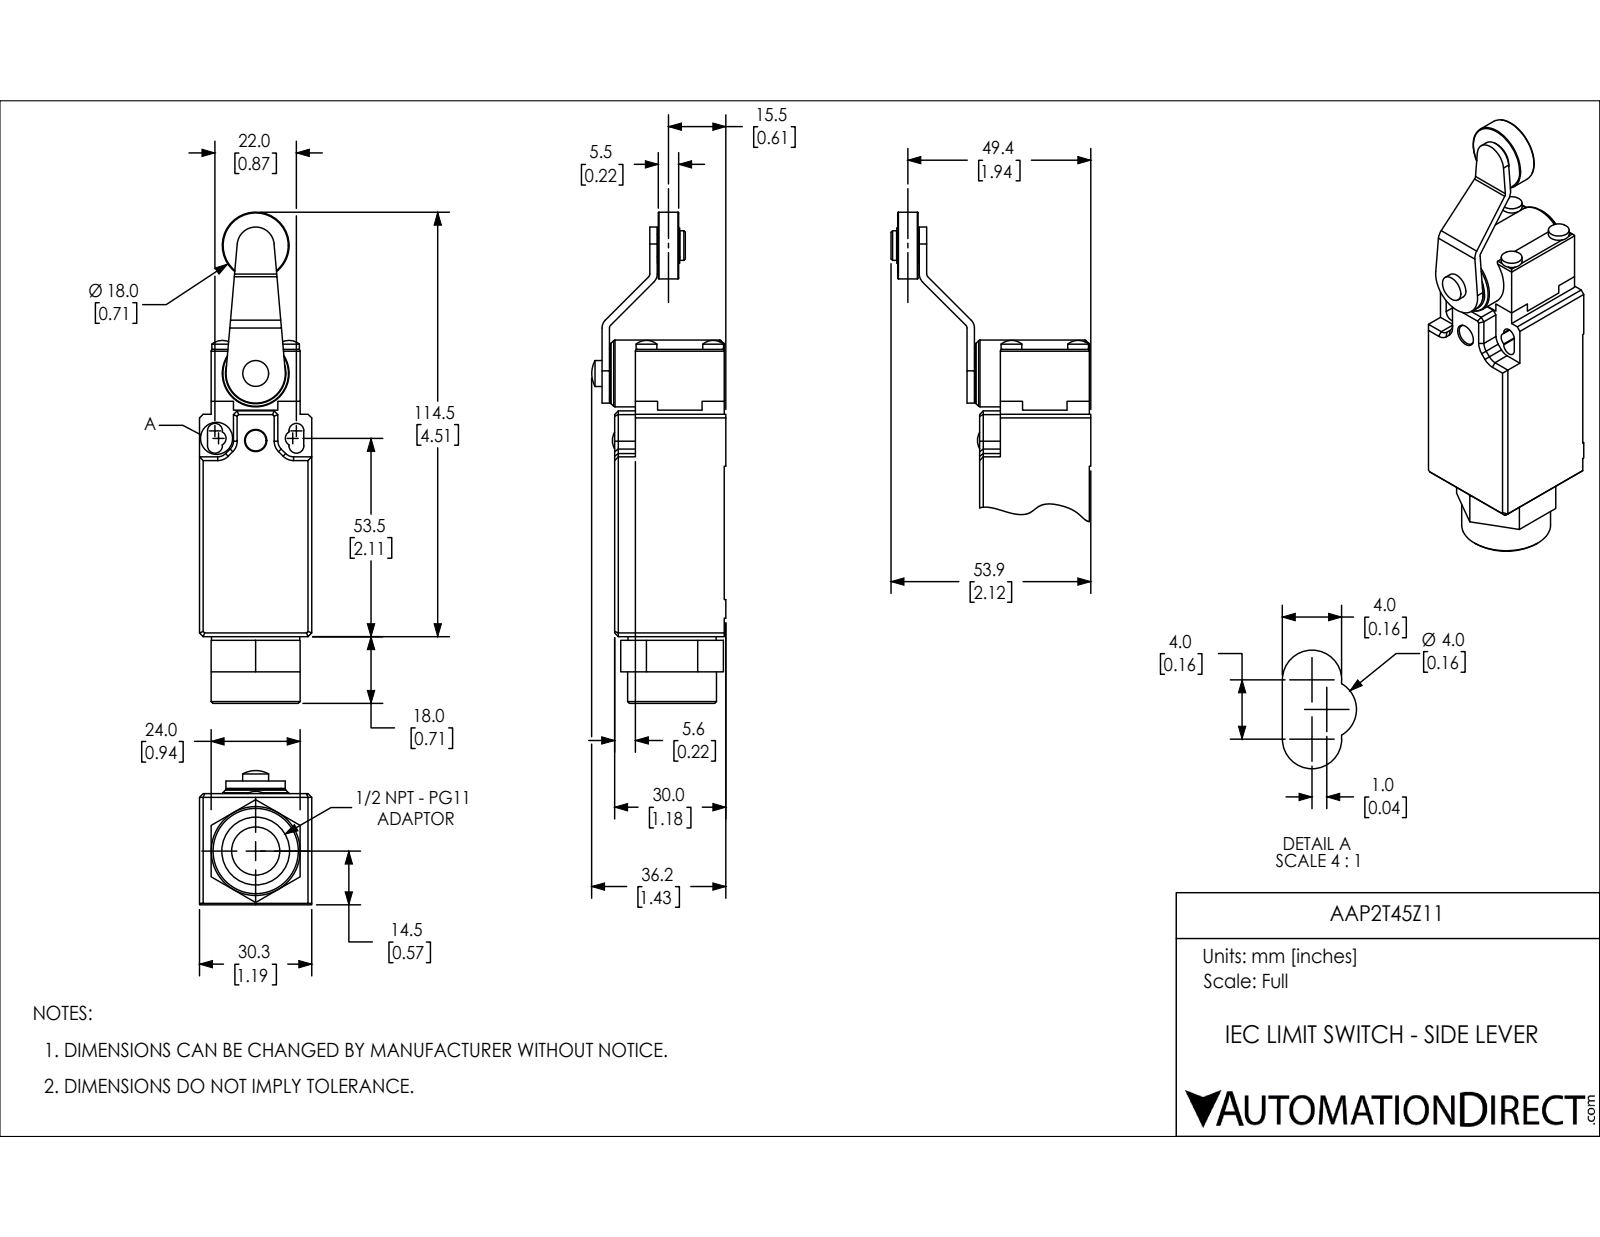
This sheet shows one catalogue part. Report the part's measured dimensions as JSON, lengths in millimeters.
{"part_name": "AAP2T45Z11", "step_written_by": "SolidWorks 2018 (AUTOMOTIVE_DESIGN)", "units": "millimeters", "bodies": {"solids": 5, "faces": 269, "planar": 134, "cylindrical": 95, "other": 40}, "overall_size": [132.5, 36.2, 30.3], "volume_mm3": 70430, "surface_area_mm2": 20370, "round_holes": [[6, 1], [13, 1], [17, 1], [18.3, 1], [18.8, 1], [19, 1]], "round_bosses_or_shafts": [[5.6, 5], [18, 2], [24, 1], [23.8, 1], [18.4, 1], [14.9, 1], [13.5, 1], [9.5, 1]], "partial_cylinders_radius": [[2, 6], [3, 6], [0.5, 4], [1, 2], [5, 1], [8, 1], [10, 1], [10.2, 1]], "face_to_face_distances": [30.3, 29.6, 24, 3.1, 27.2, 7, 1, 61.1, 6, 2]}
